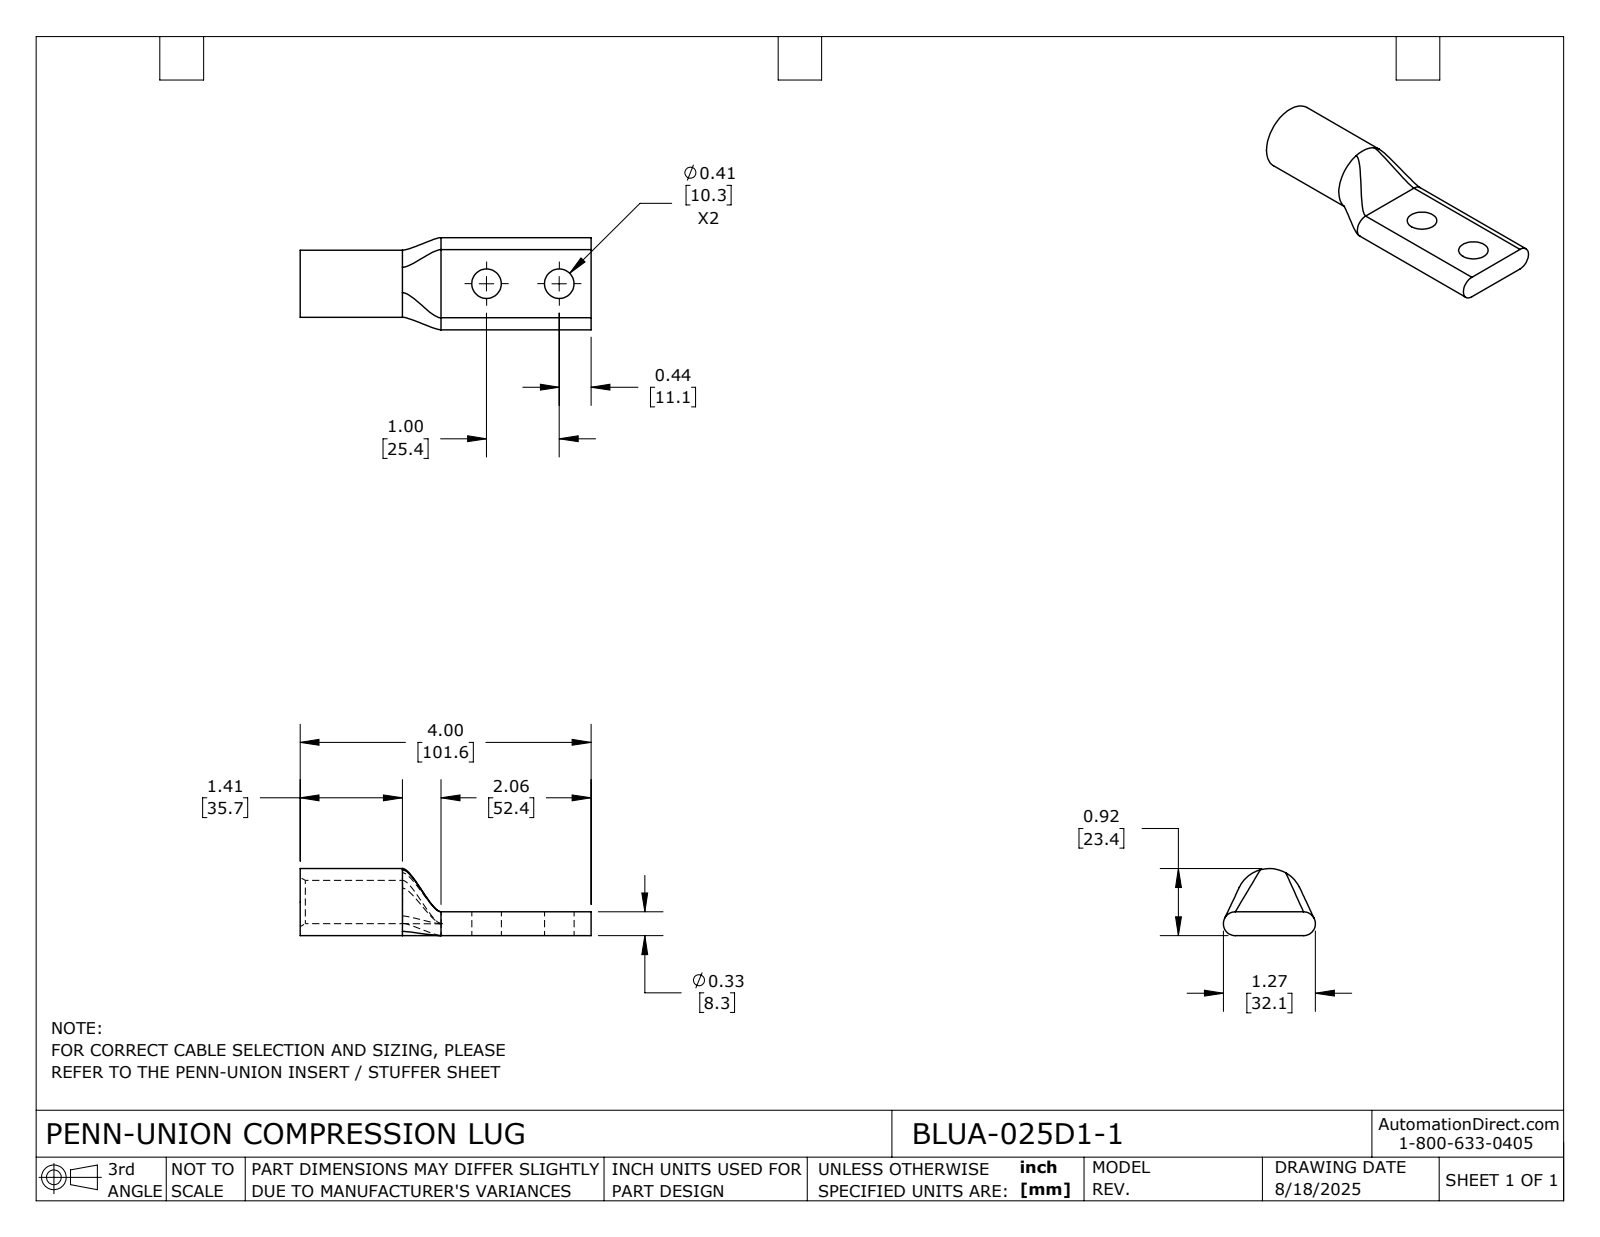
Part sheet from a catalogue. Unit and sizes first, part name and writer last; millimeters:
Units: millimetres
Overall size (bounding box): 101.6 × 32.2 × 23.4
Round holes (diameter × count): ⌀10.3 ×2, ⌀15.1 ×1
Round bosses / shafts (diameter × count): ⌀23.4 ×1
Partial cylindrical surfaces — rounded edges, fillets, slot ends (radius × count): R4.2 ×2
Main face-to-face distances: 8.3, 101.6, 49.2, 52.4
Hole centre spacings: 25.4
Volume: 24 200 mm³ · Surface area: 10 770 mm²
Bodies: 1 solid, 26 faces (5 planar, 11 cylindrical, 10 other)
Part name (STEP PRODUCT): BLUA-025D1-1
STEP written by: SolidWorks 2024 (CONFIG_CONTROL_DESIGN)
